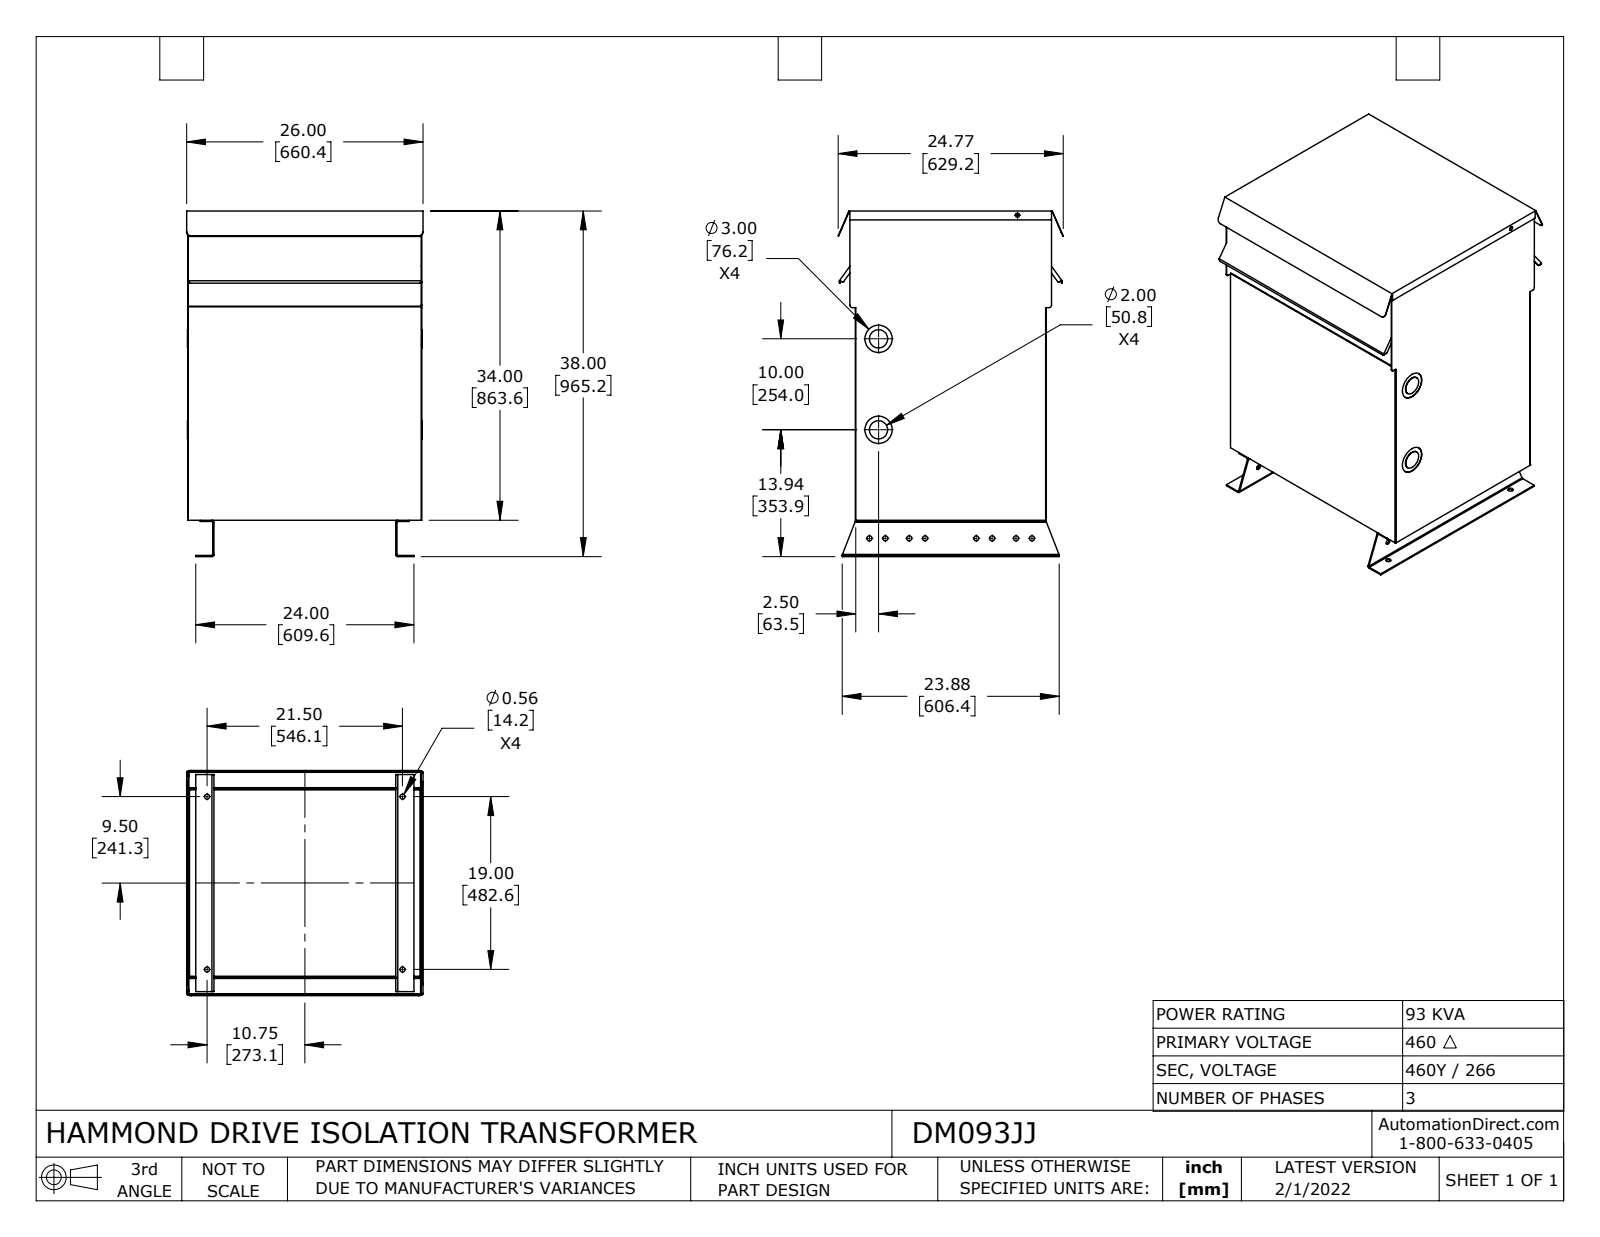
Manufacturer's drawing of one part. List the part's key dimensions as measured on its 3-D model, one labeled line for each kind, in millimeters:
Part name (STEP PRODUCT): DM093JJ
STEP written by: SolidWorks 2021 (CONFIG_CONTROL_DESIGN)
Units: millimetres
Bodies: 10 solids, 299 faces (172 planar, 127 cylindrical, 0 other)
Overall size (bounding box): 965.2 × 660.4 × 629.2
Volume: 5 957 000 mm³ · Surface area: 7 030 000 mm²
Round holes (diameter × count): ⌀14.3 ×8, ⌀14.2 ×4, ⌀11.1 ×2, ⌀76.2 ×2, ⌀11.2 ×1
Round bosses / shafts (diameter × count): ⌀50.8 ×2
Partial cylindrical surfaces — rounded edges, fillets, slot ends (radius × count): R1.5 ×6, R3.4 ×6, R1.5 ×4, R2.3 ×4, R3 ×4, R3.2 ×4, R5.7 ×4, R12.7 ×4
Main face-to-face distances: 1.5, 652.3, 531.7, 530.2, 653.8, 650.7, 1.9, 533.2, 863.6, 862.1
Hole centre spacings: 44.5, 111.1, 298.5, 254, 66.7, 155.6, 187.3, 342.9
